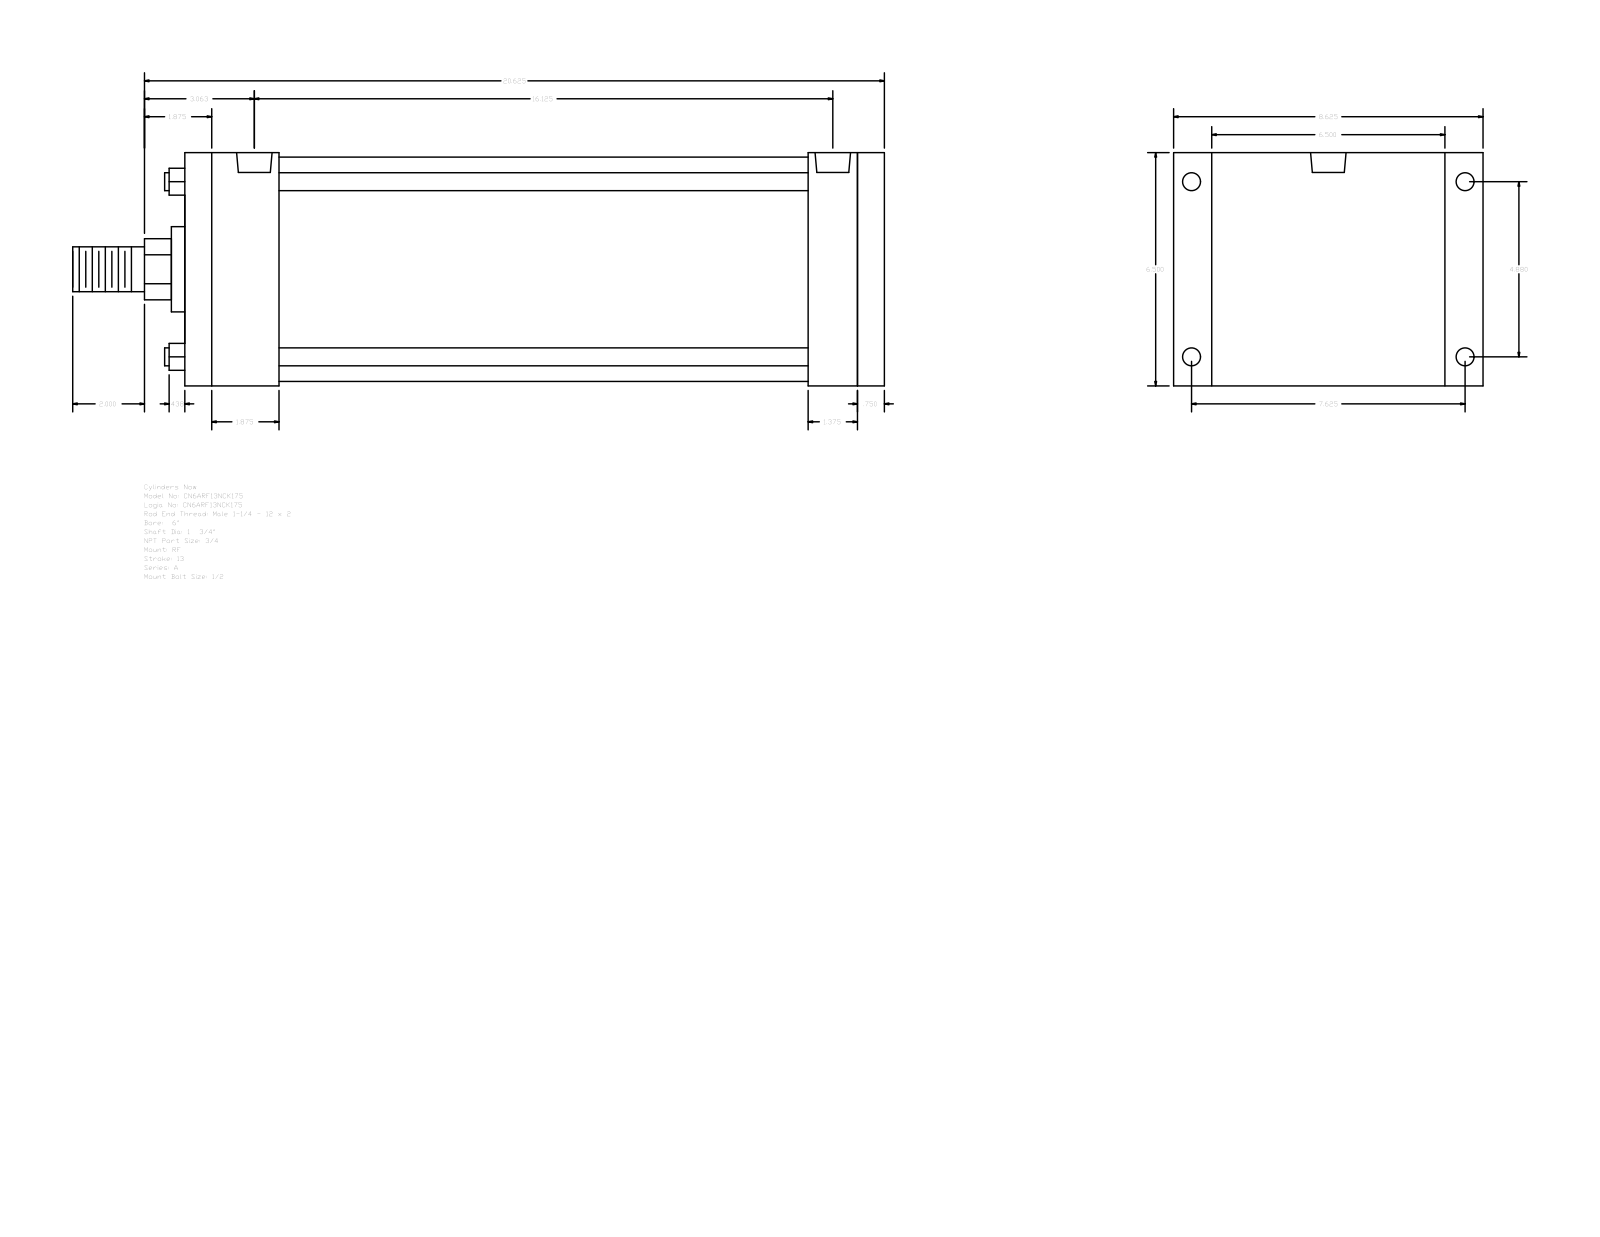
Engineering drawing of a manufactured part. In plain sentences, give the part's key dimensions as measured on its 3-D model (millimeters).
The part is named "A_RF__0600_1.75". Its 3-D file was written by "GSSL Pune (CONFIG_CONTROL_DESIGN)". It is 0 solids with 92 faces: 64 planar, 28 cylindrical and 0 other. Overall it measures 574.67 by 219.07 by 165.1 millimeters. Round holes: 4 of diameter 12.7, 4 of diameter 15.08, 2 of diameter 25.12. Round bosses or shafts: 4 of diameter 12.7, 1 of diameter 158.75, 1 of diameter 60.33, 1 of diameter 44.45, 1 of diameter 31.75. Partial cylindrical surfaces (rounded edges, fillets, slot ends): 1 of radius 21.63. The main face-to-face distances are 165.1, 495.31, 476.25, 19.06, 66.68, 409.57, 428.63, 441.33, 374.65, 34.92. The hole center spacings are 5.56, 123.96, 193.68, 229.95, 398.45, 404.01, 409.57.
